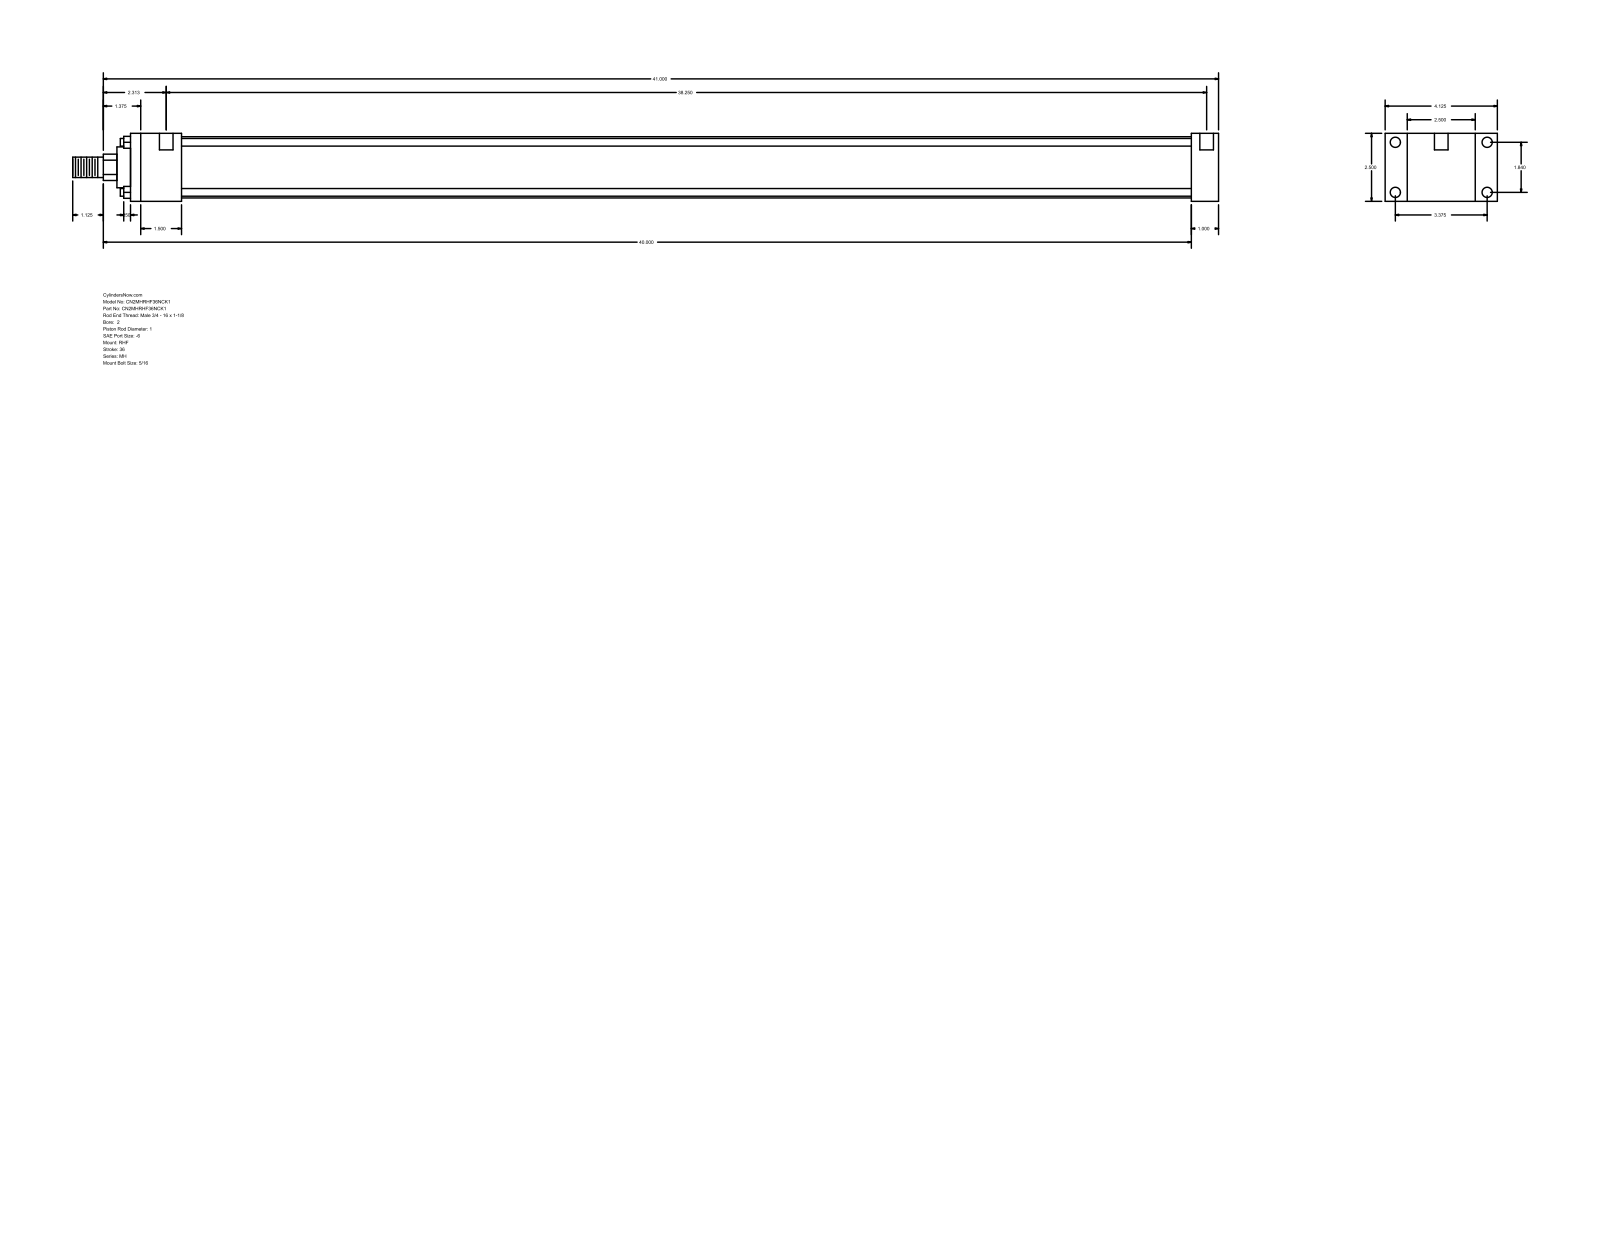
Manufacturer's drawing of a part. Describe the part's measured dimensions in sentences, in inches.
The part is named "MH_RHF__0200_1". Its 3-D file was written by "GSSL Pune (CONFIG_CONTROL_DESIGN)". It is 0 solids with 88 faces: 60 planar, 28 cylindrical and 0 other. Overall it measures 42.125 by 4.125 by 2.5 inches. Round holes: 4 of diameter 0.219, 4 of diameter 0.375, 2 of diameter 0.5. Round bosses or shafts: 4 of diameter 0.281, 1 of diameter 2.25, 1 of diameter 1.5, 1 of diameter 1, 1 of diameter 0.75. Partial cylindrical surfaces (rounded edges, fillets, slot ends): 1 of radius 0.484. The main face-to-face distances are 2.5, 1, 0.813, 3.313, 40, 39, 4.125, 1.875, 37.125, 38.125. The hole center spacings are 1.84, 3.375, 3.844, 38.562, 0.125, 0.187, 38.25, 38.375.
